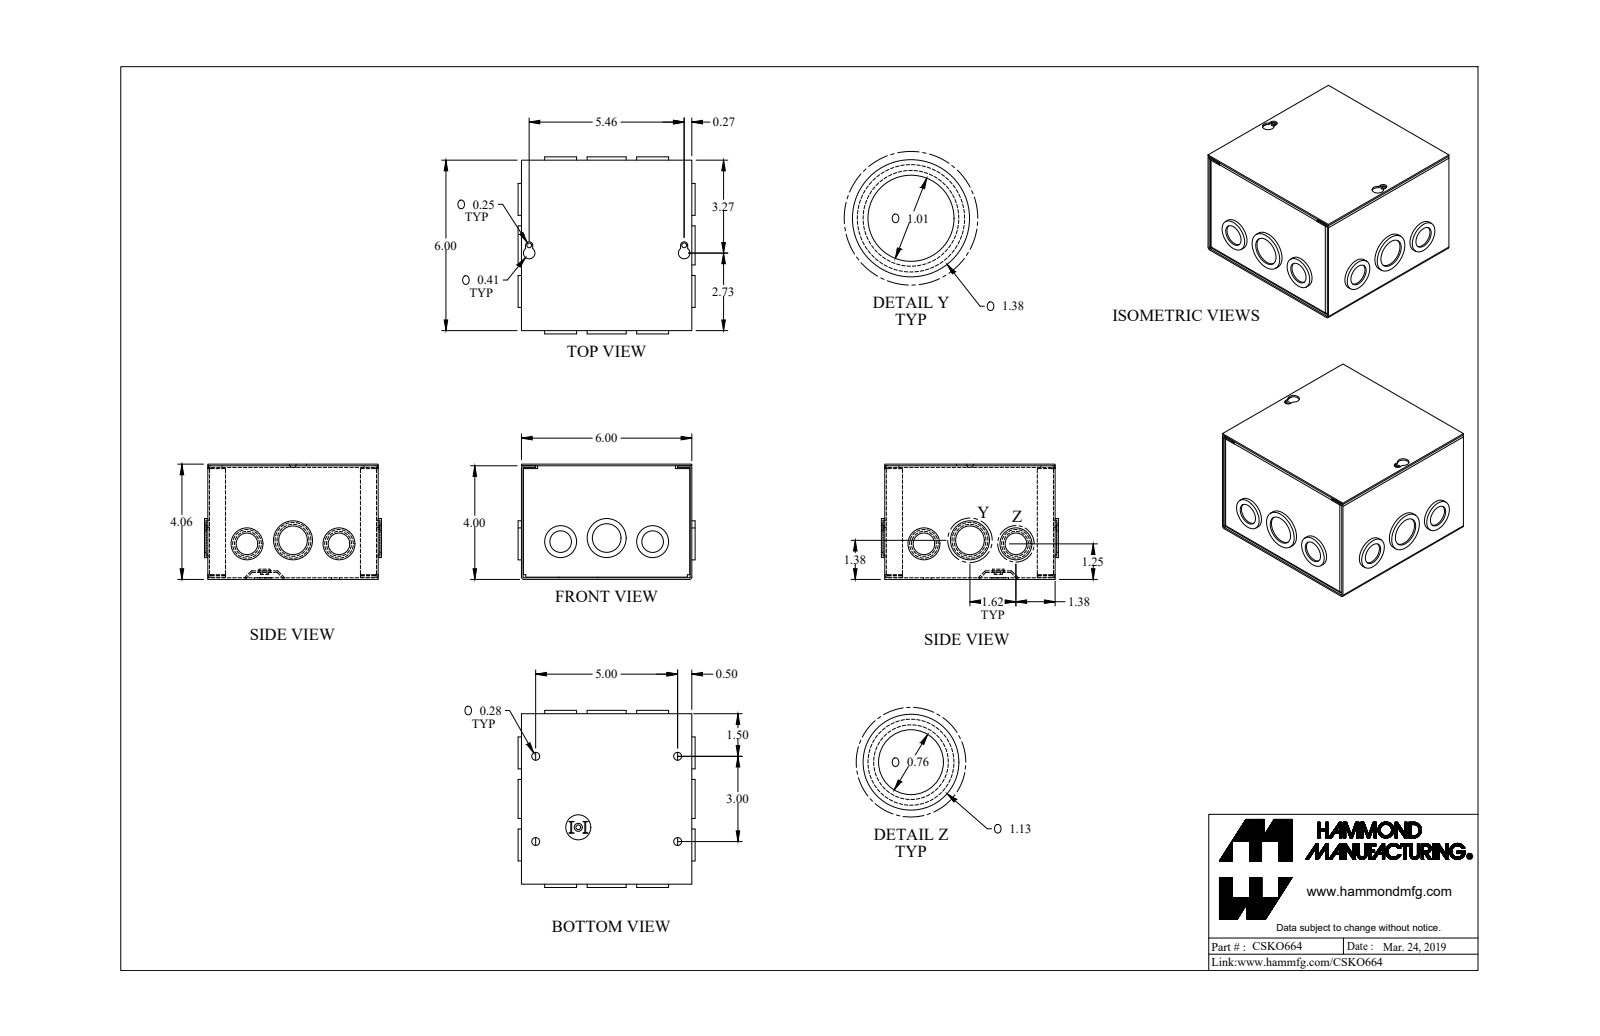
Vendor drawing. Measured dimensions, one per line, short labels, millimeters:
name: CSKO664_Default
written by: SolidWorks 2019 (CONFIG_CONTROL_DESIGN)
unit: mm
bodies: 4 solids, 333 faces (169 planar, 156 cylindrical, 8 other)
size: 158.3 × 158.3 × 103
volume: 182 200 mm³; area: 256 100 mm²
holes: 6× ⌀25.7, 4× ⌀7.1, 4× ⌀19.3, 3× ⌀4.3, 2× ⌀32, 1× ⌀12.7
bosses: 5× ⌀28.6, 4× ⌀22.2, 3× ⌀22.2, 2× ⌀34.9, 1× ⌀28.6, 1× ⌀12.5, 1× ⌀7.2
rounds: 12× R0.7, 12× R2.2, 8× R1.4, 2× R3.2, 2× R5.2
face distances: 1.4, 151, 101.6, 152.4, 100.2, 149.5, 103, 1.8, 149.2, 2.9
hole spacings: 38.5, 41.3, 138.2, 76.2, 82.3, 127, 148.1, 38.1
